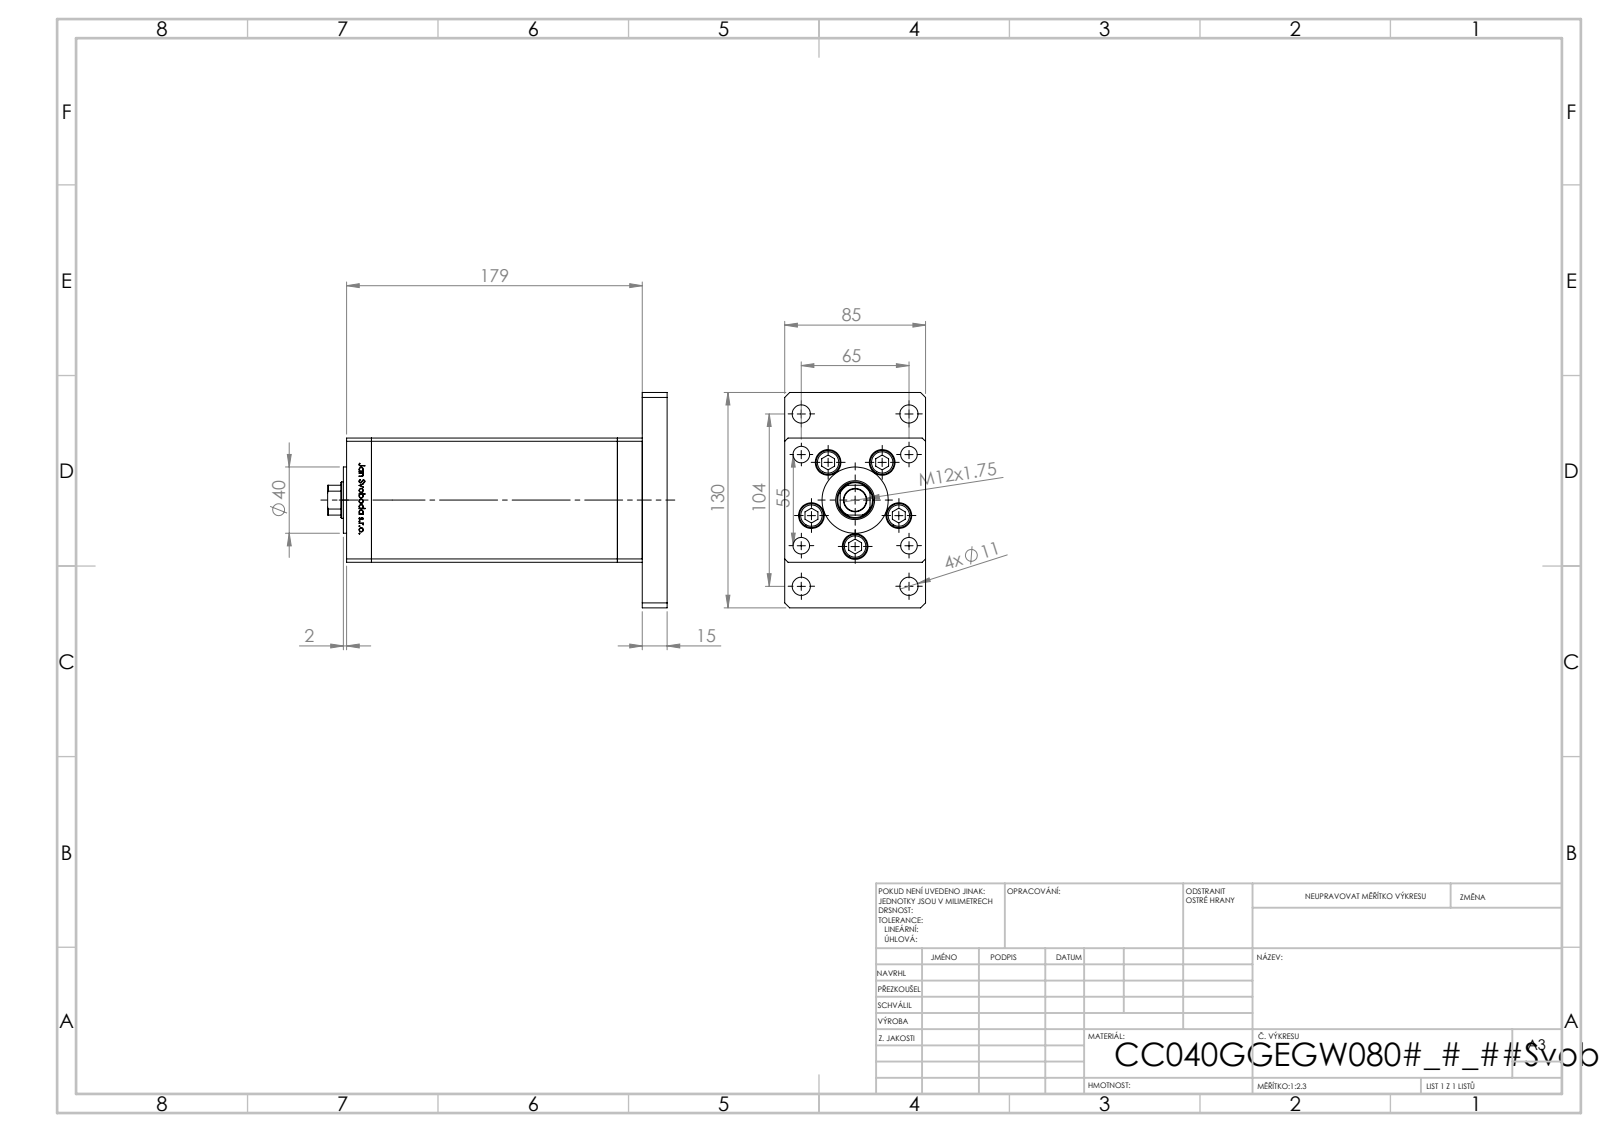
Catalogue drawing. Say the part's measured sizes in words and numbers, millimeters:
The part is named "V220C_G_MIDDLE; V220C_VC_G; V220C_F; V220C BACK_G (+2 more)". Its 3-D file was written by "SolidWorks 2019 (CONFIG_CONTROL_DESIGN)". It is 19 solids with 1313 faces: 518 planar, 189 cylindrical and 606 other. Overall it measures 205 by 130 by 85 millimeters. Its volume is 1 158 000 cubic millimeters and its surface area 197 576 square millimeters. Round holes: 9 of diameter 10, 9 of diameter 11, 5 of diameter 15.5, 4 of diameter 14.5, 2 of diameter 2, 2 of diameter 13.16, 1 of diameter 13.5, 1 of diameter 22, 1 of diameter 23.5, 1 of diameter 56. Round bosses or shafts: 9 of diameter 8, 5 of diameter 14.5, 1 of diameter 40. Partial cylindrical surfaces (rounded edges, fillets, slot ends): 2 of radius 0.93, 1 of radius 10.5. The main face-to-face distances are 15, 85, 163.5, 178.5, 75, 148.5, 30, 2, 176.5, 193.5. The hole center spacings are 28, 24.5, 42.57, 61.32, 65, 69.46, 79.5, 102.69.
